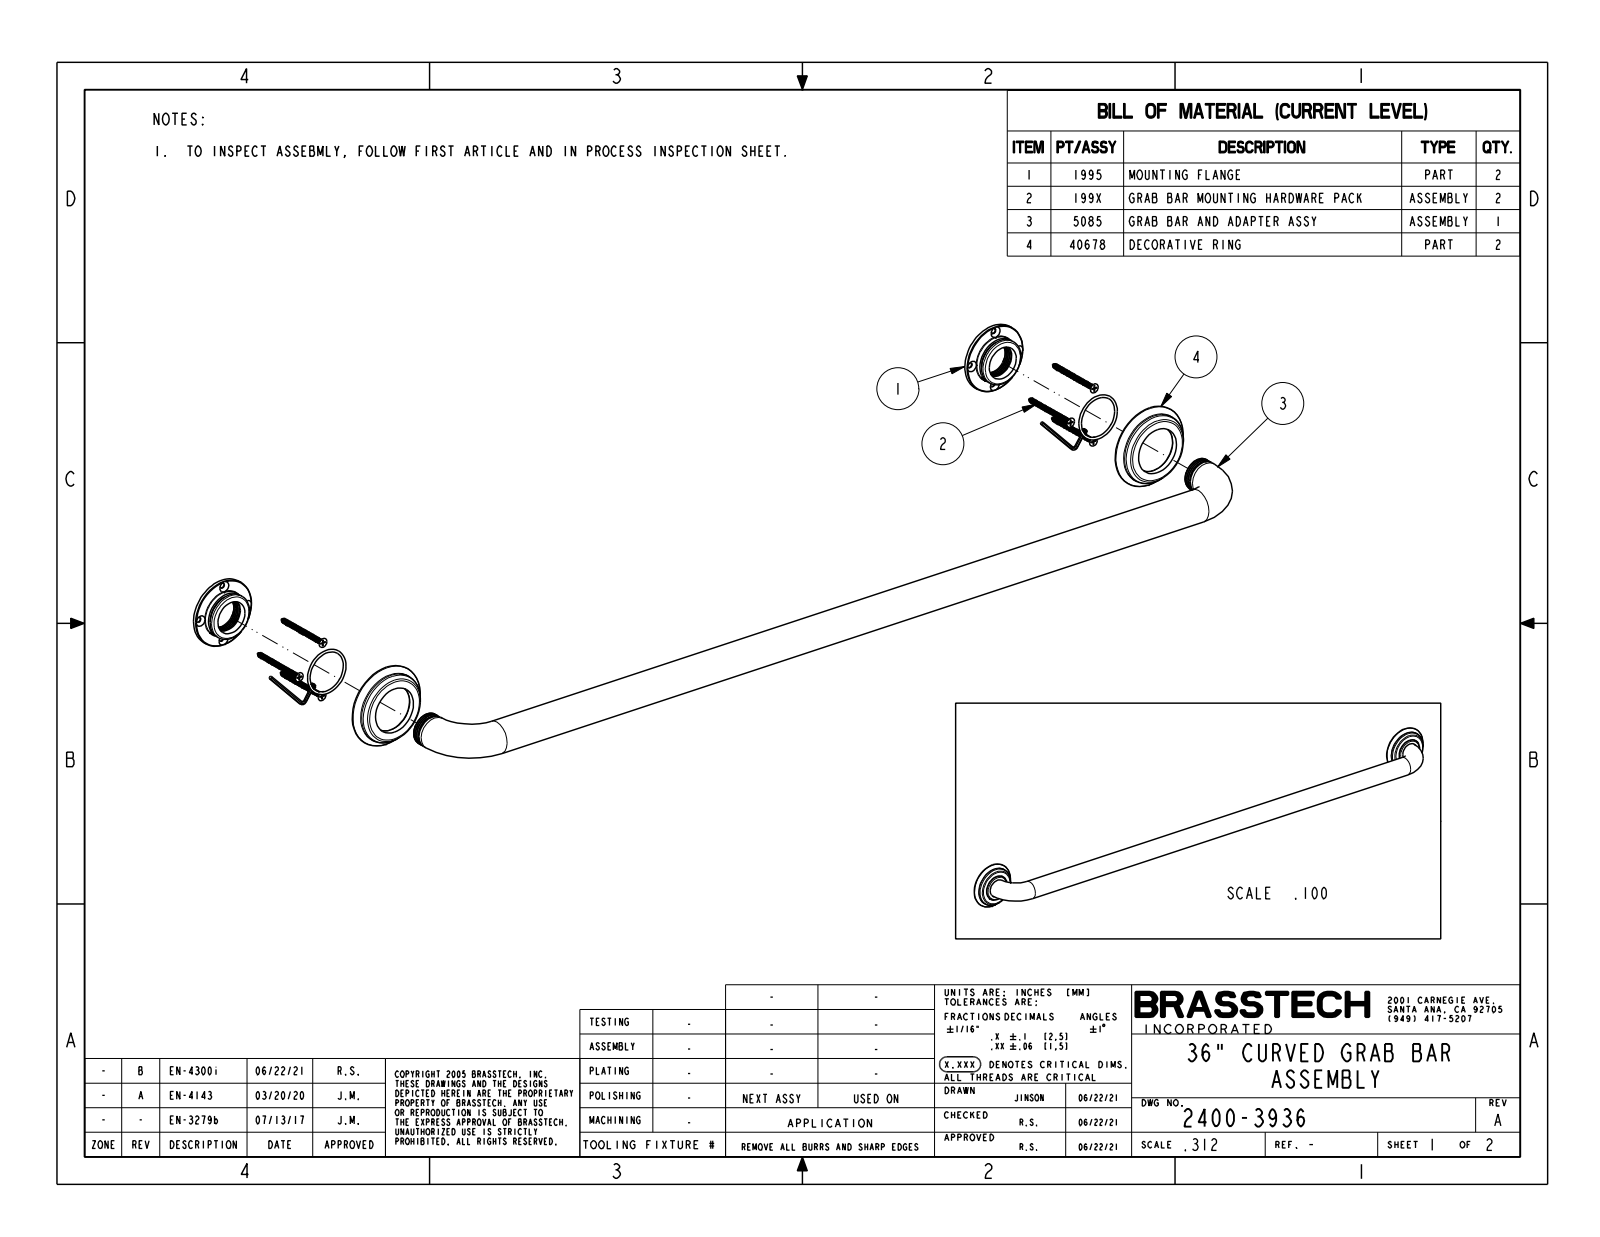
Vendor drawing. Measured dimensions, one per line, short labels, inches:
name: 2400-3936
written by: CREO PARAMETRIC BY PTC INC, 2018400 (CONFIG_CONTROL_DESIGN)
unit: in
bodies: 1 solid, 44 faces (6 planar, 6 cylindrical, 32 other)
size: 39.154 × 3.154 × 2.75
volume: 52.95 in³; area: 182.2 in²
bosses: 2× ⌀1.75, 1× ⌀1.25
face distances: 0.525, 0.6, 0.075
